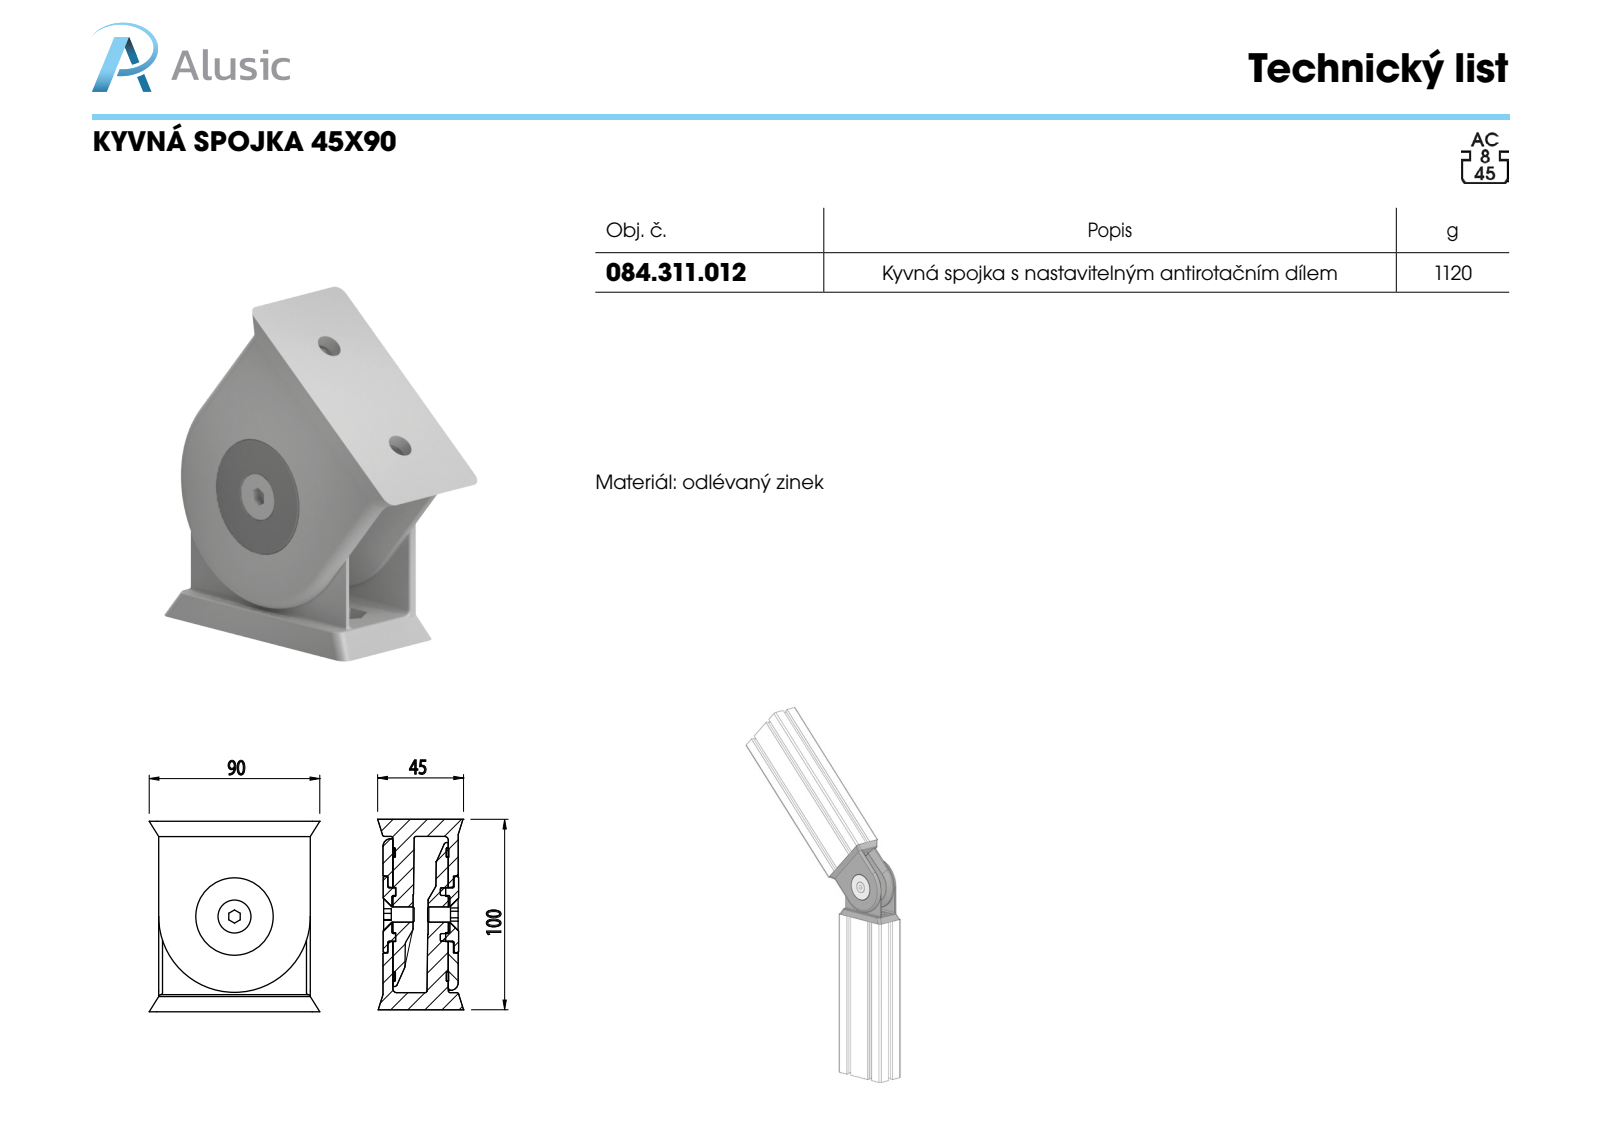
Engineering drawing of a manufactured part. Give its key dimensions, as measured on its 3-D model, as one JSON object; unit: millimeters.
{"part_name": "093gr02_093 g r02_3; 093g4080r01_093 g 4590 r02_2; 4din7991m0816e_4din7991m0816e_2; 093gr01_093 g r01_3 (+1 more)", "step_written_by": "SolidWorks 2011 (CONFIG_CONTROL_DESIGN)", "units": "millimeters", "bodies": {"solids": 8, "faces": 540, "planar": 178, "cylindrical": 152, "other": 210}, "overall_size": [117.1, 111.26, 44.8], "volume_mm3": 188002, "surface_area_mm2": 78924, "round_holes": [[6.8, 1], [9, 1], [20, 1], [60.4, 1], [70, 1]], "round_bosses_or_shafts": [[2, 4], [79.6, 1], [75.6, 1], [69.6, 1], [60, 1], [40, 1], [28, 1], [16, 1]], "partial_cylinders_radius": [[1, 44], [2, 18], [4, 12], [1.5, 4], [2.5, 4]], "face_to_face_distances": [5.2, 29.1, 5.5, 34.3, 34.6, 29.4, 34.5, 28.8, 39.8, 6.5]}
